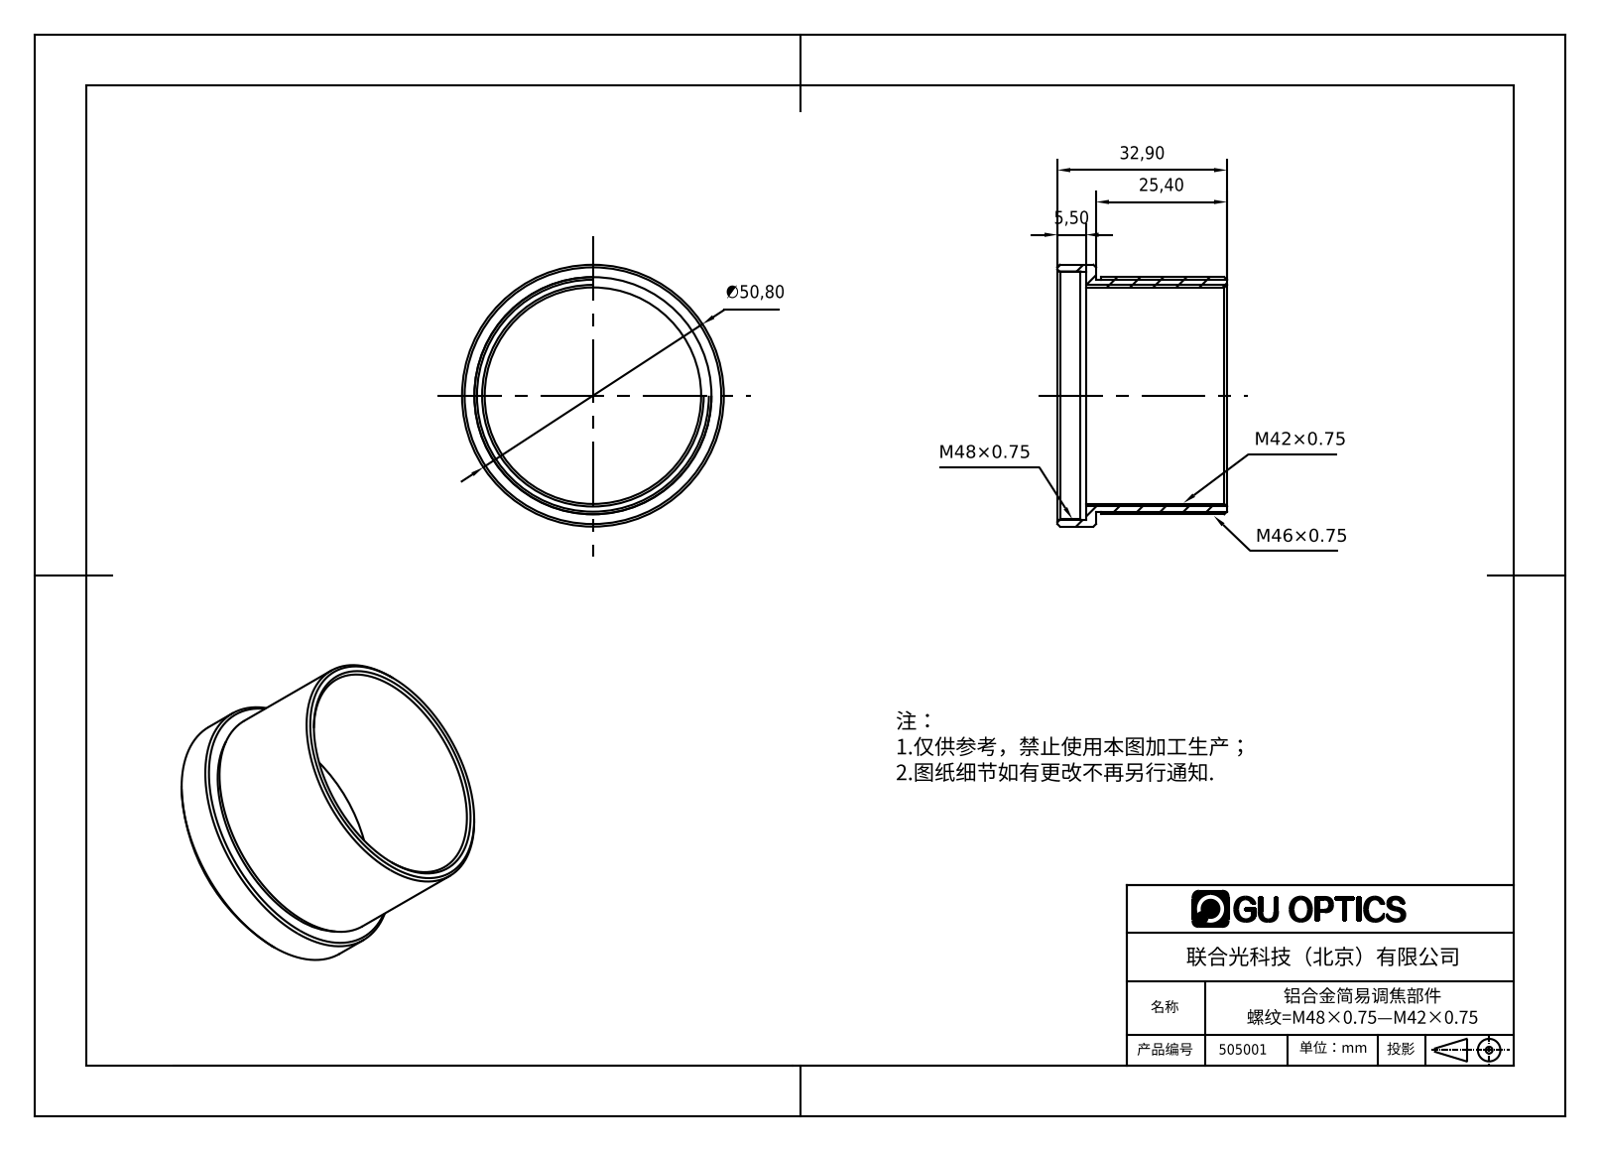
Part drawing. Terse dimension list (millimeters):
name: 505001
written by: SolidWorks 2016 (CONFIG_CONTROL_DESIGN)
unit: mm
bodies: 1 solid, 28 faces (6 planar, 12 cylindrical, 10 other)
size: 50.8 × 50.8 × 32.9
volume: 9 320 mm³; area: 10 547 mm²
holes: 1× ⌀42, 1× ⌀48, 1× ⌀48.2
bosses: 1× ⌀50.8, 1× ⌀46, 1× ⌀45
face distances: 2, 27.4, 25.4, 1, 3, 24.4, 5.5, 7.5, 8.5, 32.9
